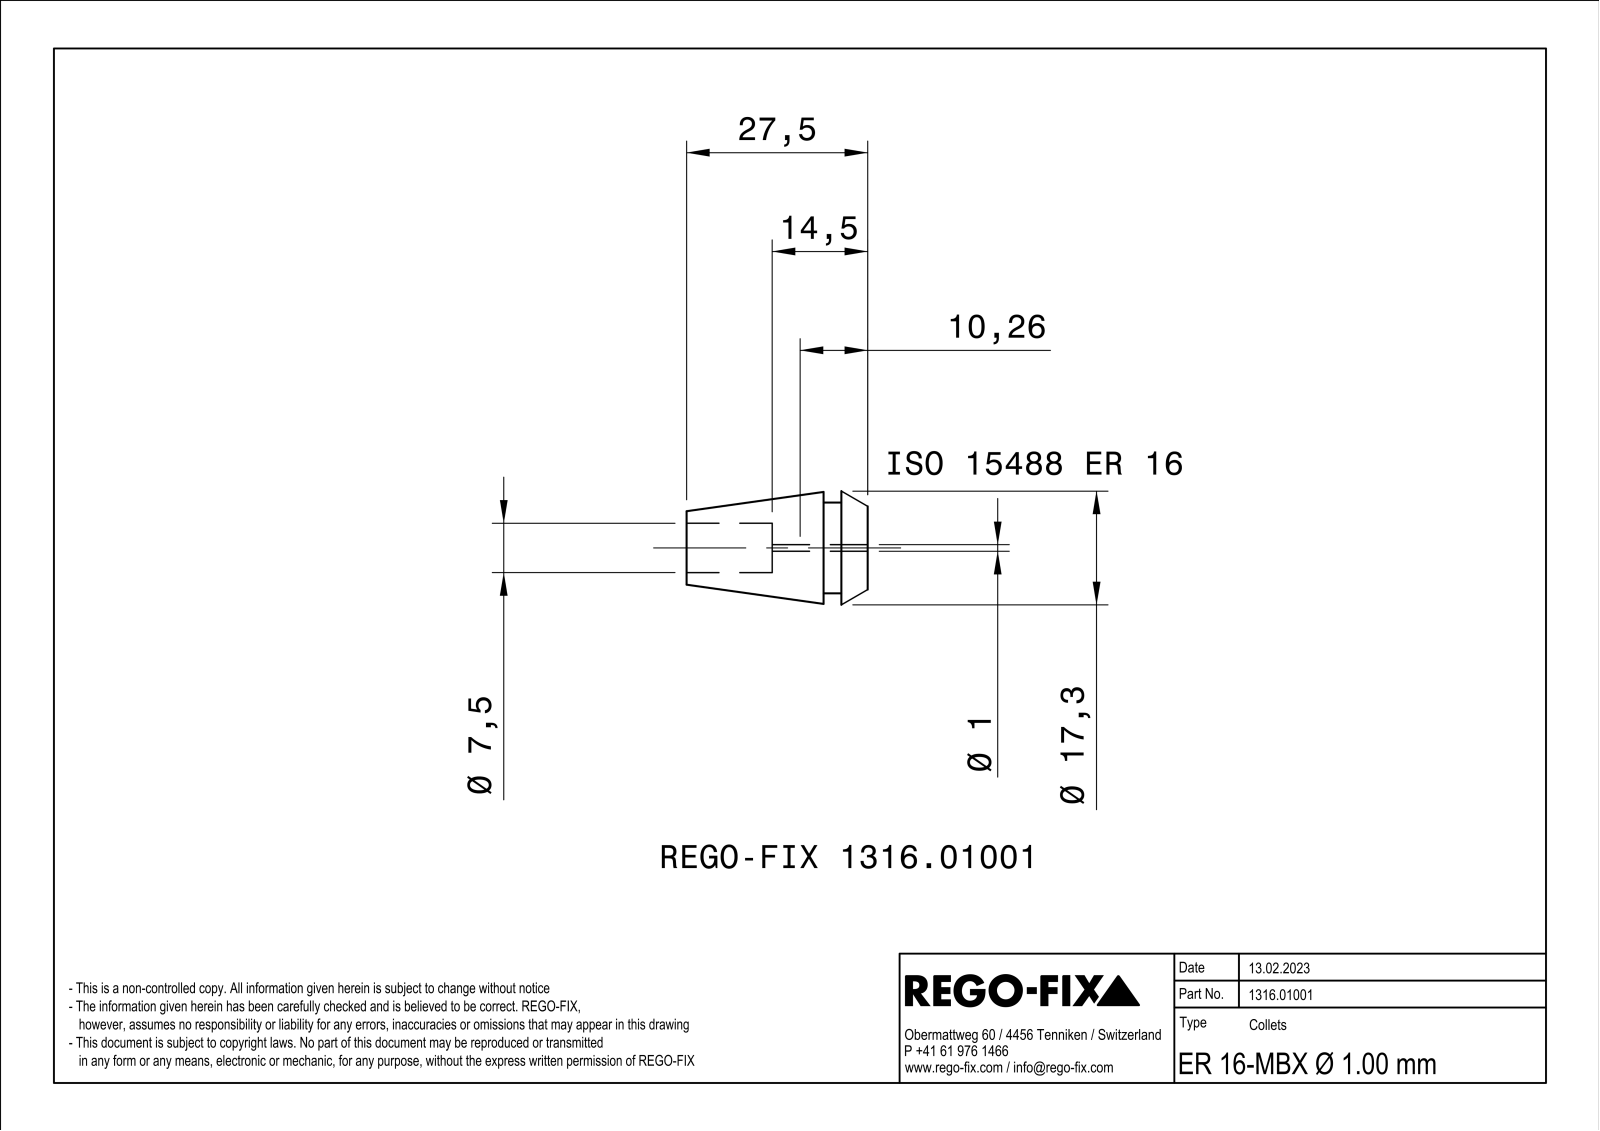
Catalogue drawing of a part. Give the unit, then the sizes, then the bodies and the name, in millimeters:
Units: millimetres
Overall size (bounding box): 27.5 × 16.91 × 16.9
Round holes (diameter × count): ⌀2 ×3, ⌀7.5 ×1
Round bosses / shafts (diameter × count): ⌀13.8 ×1
Partial cylindrical surfaces — rounded edges, fillets, slot ends (radius × count): R0.14 ×3, R25 ×3, R0.5 ×1
Main face-to-face distances: 0.54, 0.8, 6.7, 4, 2.7, 27.5, 23.5, 20.8, 14.5, 10.5
Hole centre spacings: 2.1, 3.64
Volume: 3 298 mm³ · Surface area: 3 318 mm²
Bodies: 1 solid, 109 faces (36 planar, 27 cylindrical, 46 other)
Part name (STEP PRODUCT): NOCUT
STEP written by: SIEMENS PLM Software Solid Edge ST10 (AUTOMOTIVE_DESIGN)
